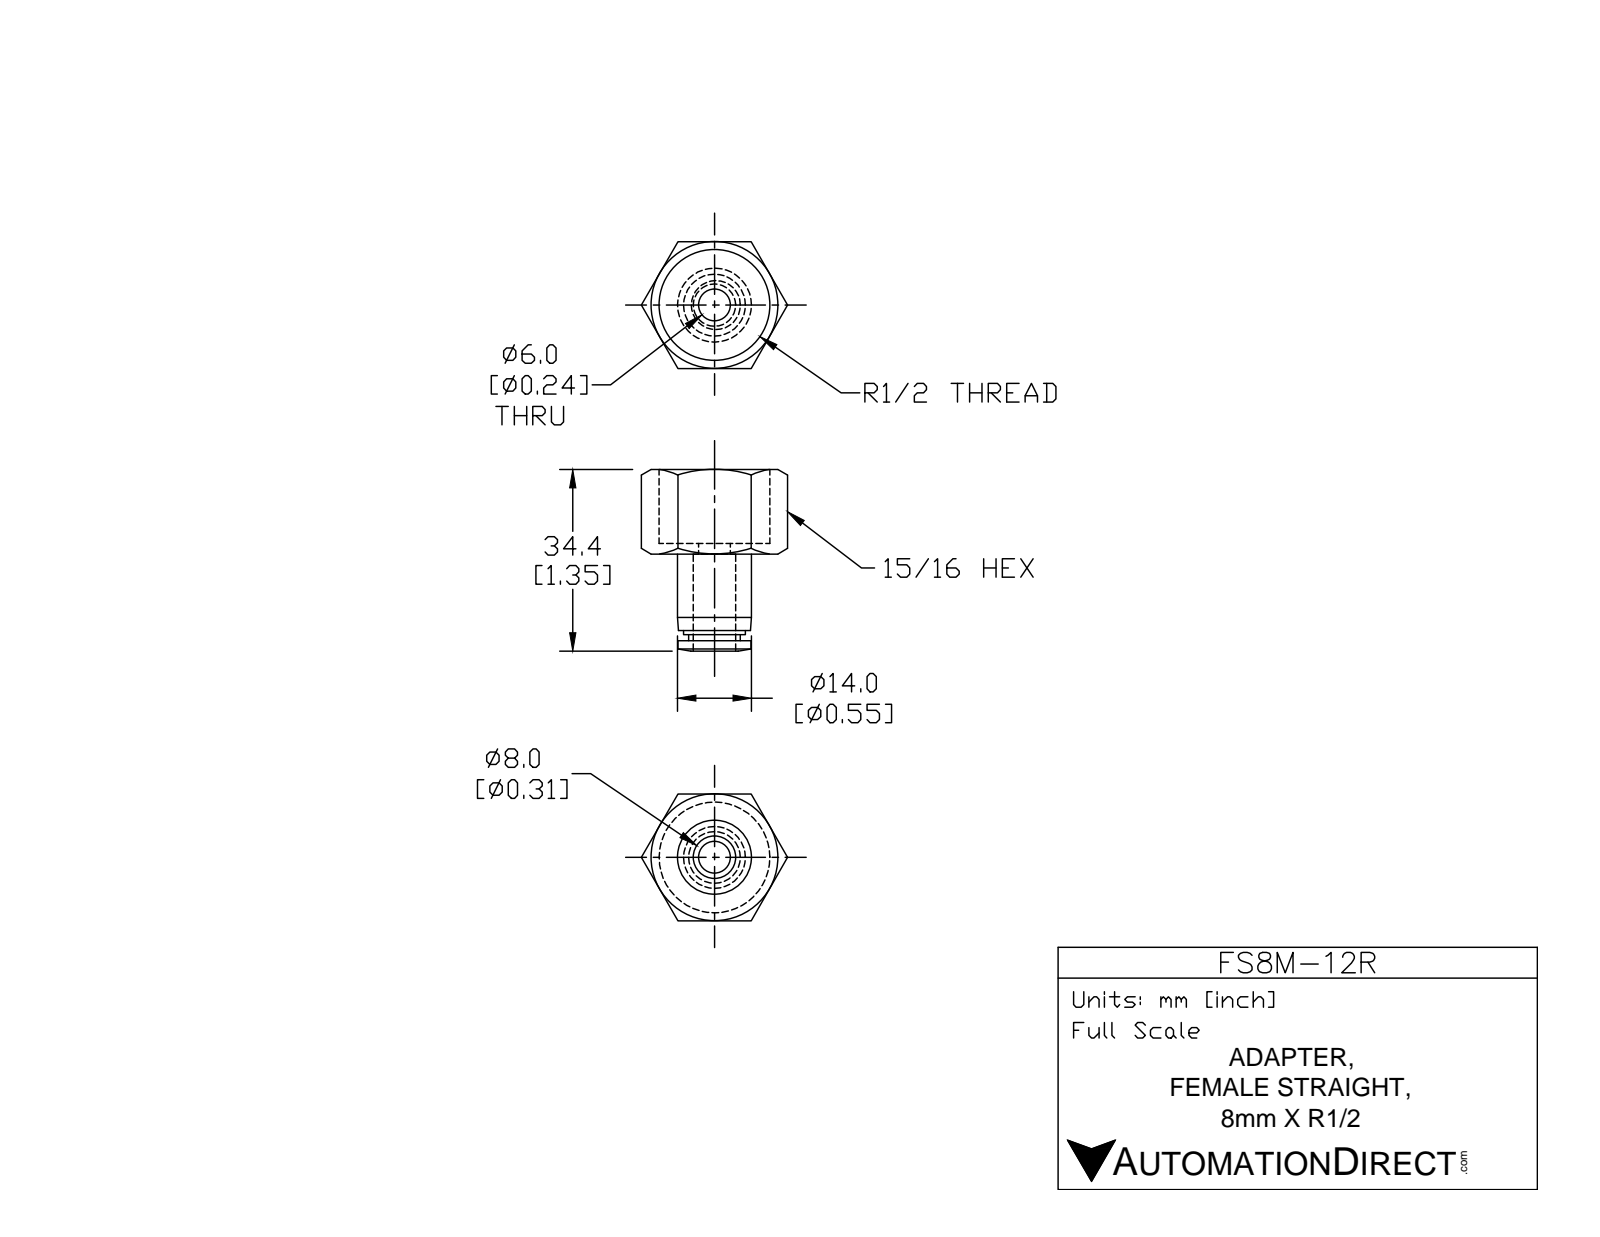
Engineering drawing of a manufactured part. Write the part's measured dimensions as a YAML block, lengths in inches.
part_name: "FS8M-12R"
step_written_by: "SolidWorks 2015 (AUTOMOTIVE_DESIGN)"
units: inches
bodies: {solids: 1, faces: 48, planar: 14, cylindrical: 12, other: 22}
overall_size: [1.354, 1.091, 0.945]
volume: 0.301
surface_area: 7.011
round_holes:
  - {diameter: 0.236, count: 1}
  - {diameter: 0.327, count: 1}
round_bosses_or_shafts:
  - {diameter: 0.551, count: 1}
  - {diameter: 0.543, count: 1}
  - {diameter: 0.461, count: 1}
  - {diameter: 0.386, count: 1}
face_to_face_distances: [0.945, 0.079, 0.551, 0.63, 0.724, 1.276, 0.646, 1.201, 0.65, 0.571]
